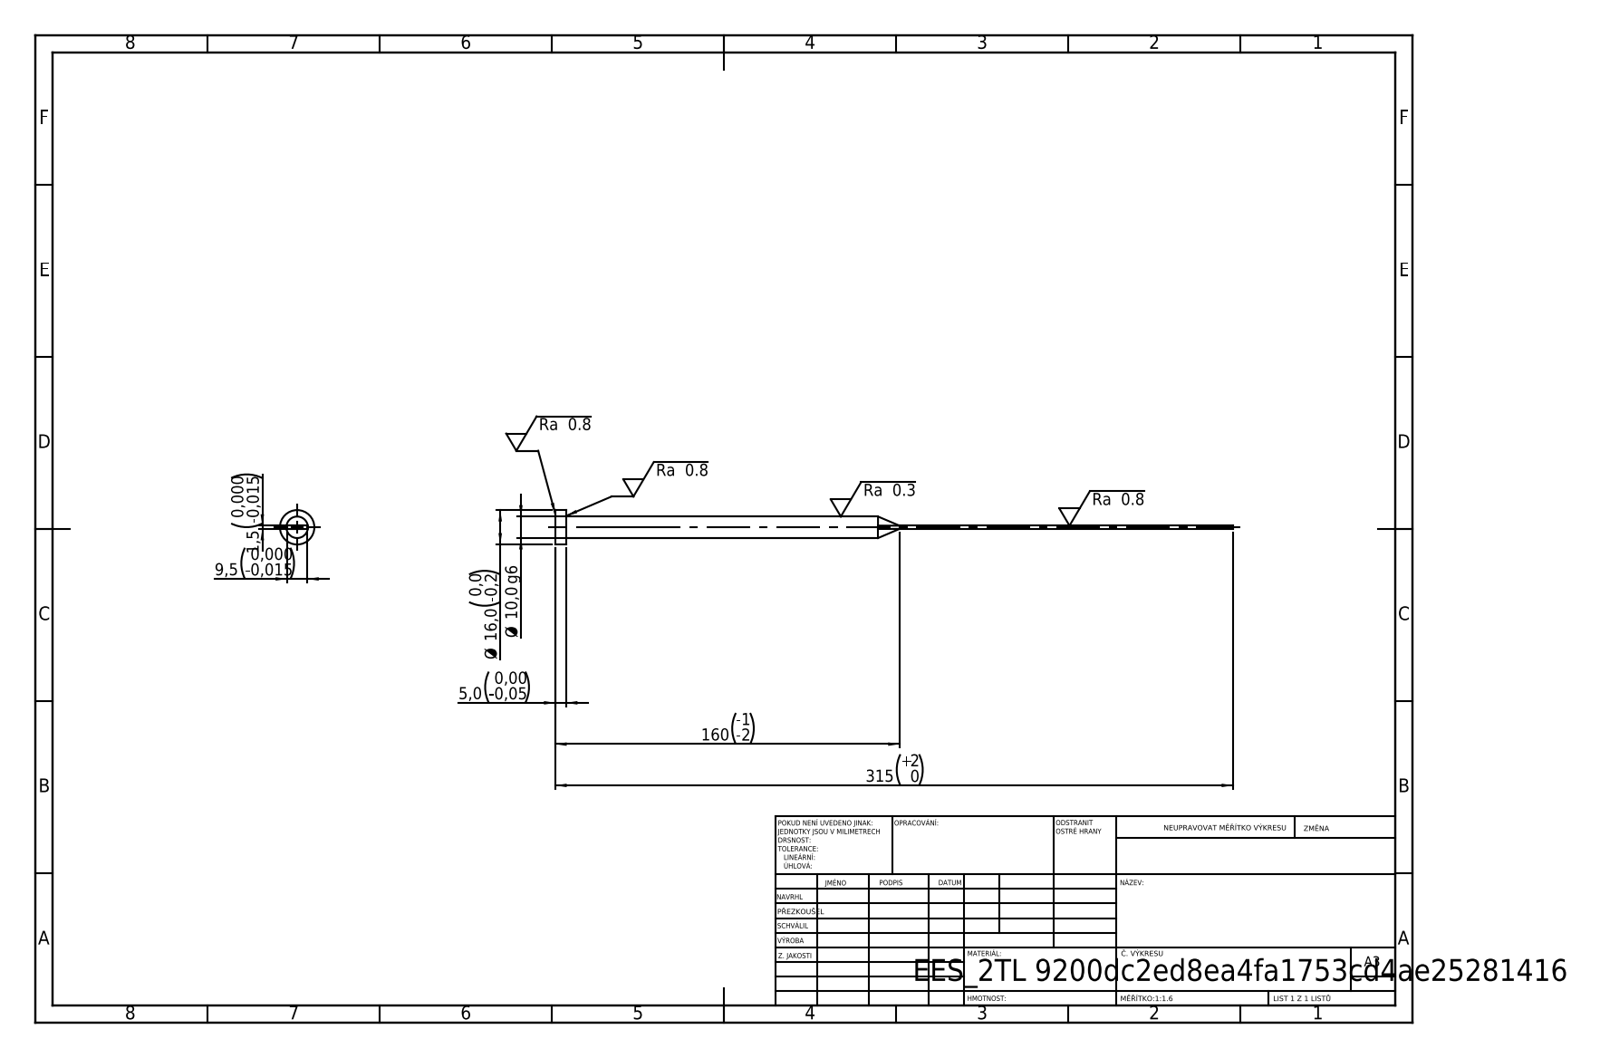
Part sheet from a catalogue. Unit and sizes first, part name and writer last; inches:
Units: inches
Overall size (bounding box): 12.402 × 0.63 × 0.63
Round bosses / shafts (diameter × count): ⌀0.63 ×1, ⌀0.394 ×1
Main face-to-face distances: 0.059, 0.374, 0.197, 12.402, 12.205
Volume: 0.918 in³ · Surface area: 13.67 in²
Bodies: 1 solid, 15 faces (7 planar, 4 cylindrical, 4 other)
STEP written by: SolidWorks 2019 (CONFIG_CONTROL_DESIGN)
